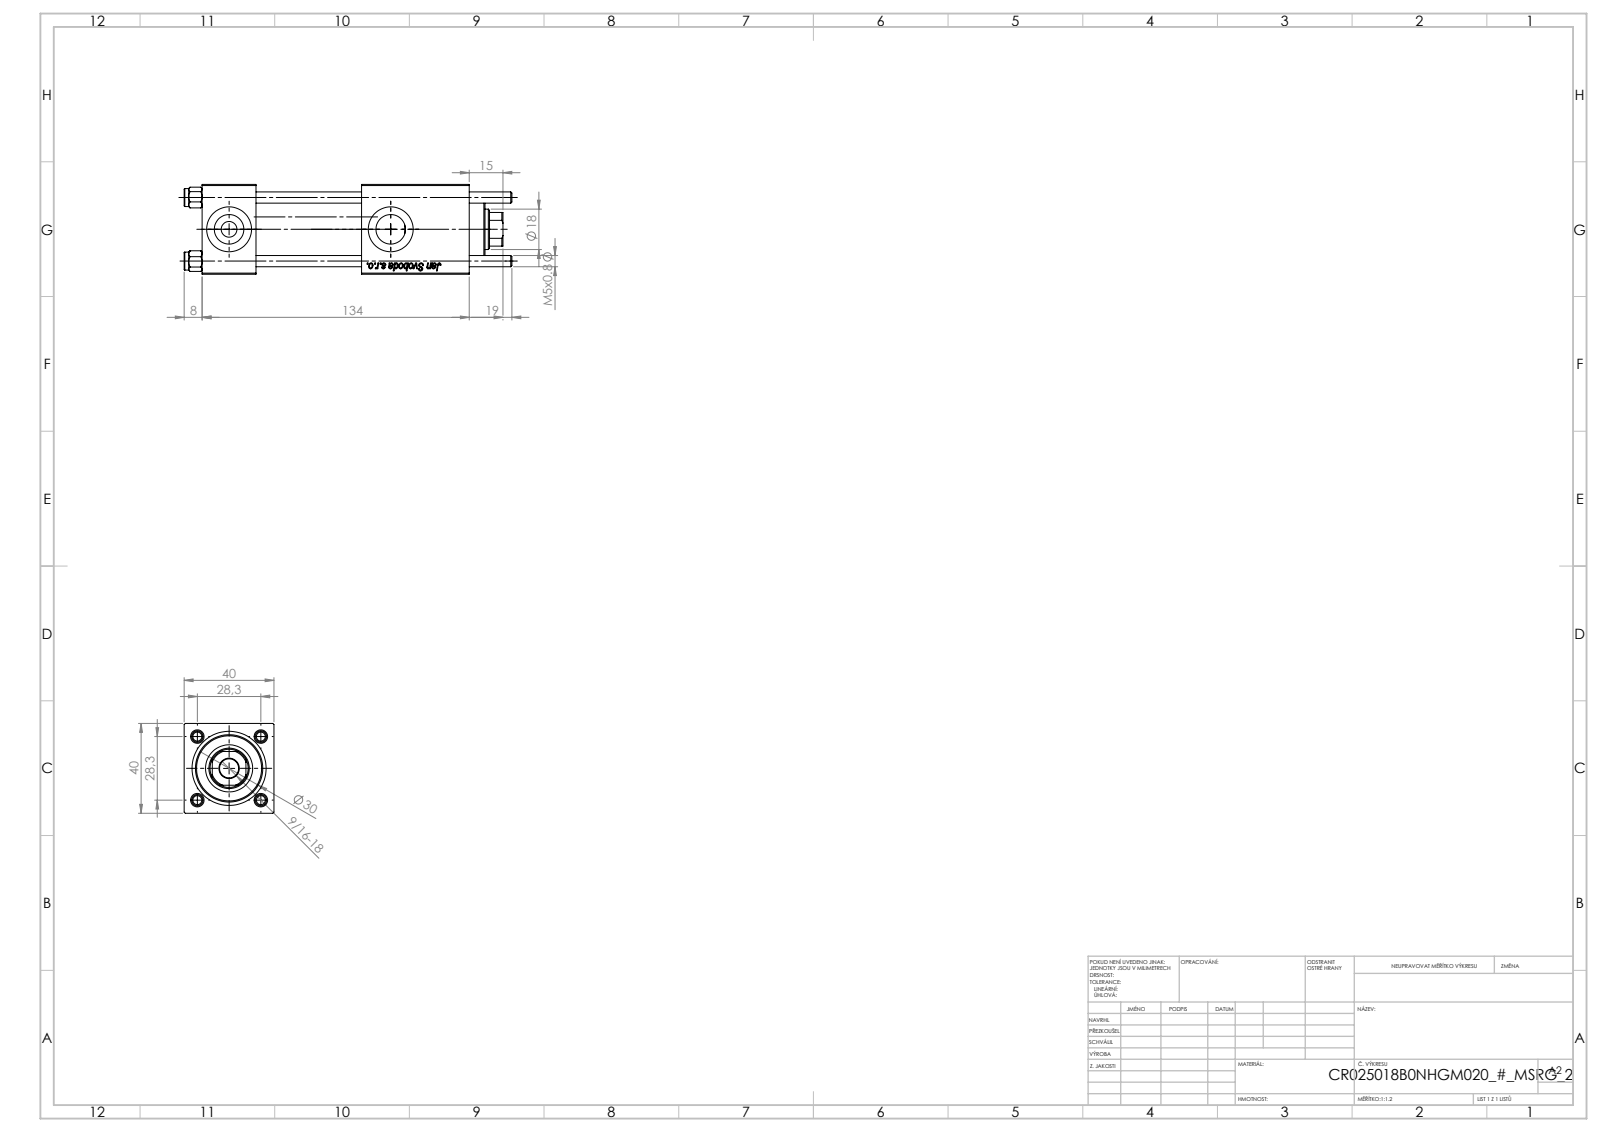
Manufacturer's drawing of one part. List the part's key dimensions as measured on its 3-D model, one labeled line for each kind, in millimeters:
Part name (STEP PRODUCT): V215CR_VCP_B; V215_VC_A; NUT_M5_B; V215CR_B-1 (+1 more)
STEP written by: SolidWorks 2019 (CONFIG_CONTROL_DESIGN)
Units: millimetres
Bodies: 11 solids, 1152 faces (428 planar, 76 cylindrical, 648 other)
Overall size (bounding box): 146 × 40 × 40
Volume: 152 491 mm³ · Surface area: 60 895 mm²
Round holes (diameter × count): ⌀5 ×4, ⌀20 ×3, ⌀7 ×2, ⌀13.16 ×2, ⌀8.5 ×1, ⌀18 ×1, ⌀21 ×1, ⌀25 ×1, ⌀30 ×1
Round bosses / shafts (diameter × count): ⌀8 ×4, ⌀31 ×1
Partial cylindrical surfaces — rounded edges, fillets, slot ends (radius × count): R8.5 ×1
Main face-to-face distances: 40, 24, 71, 47, 90.3, 66.3, 19.3, 119, 95, 48
Hole centre spacings: 20.01, 28.3, 40.02, 72
